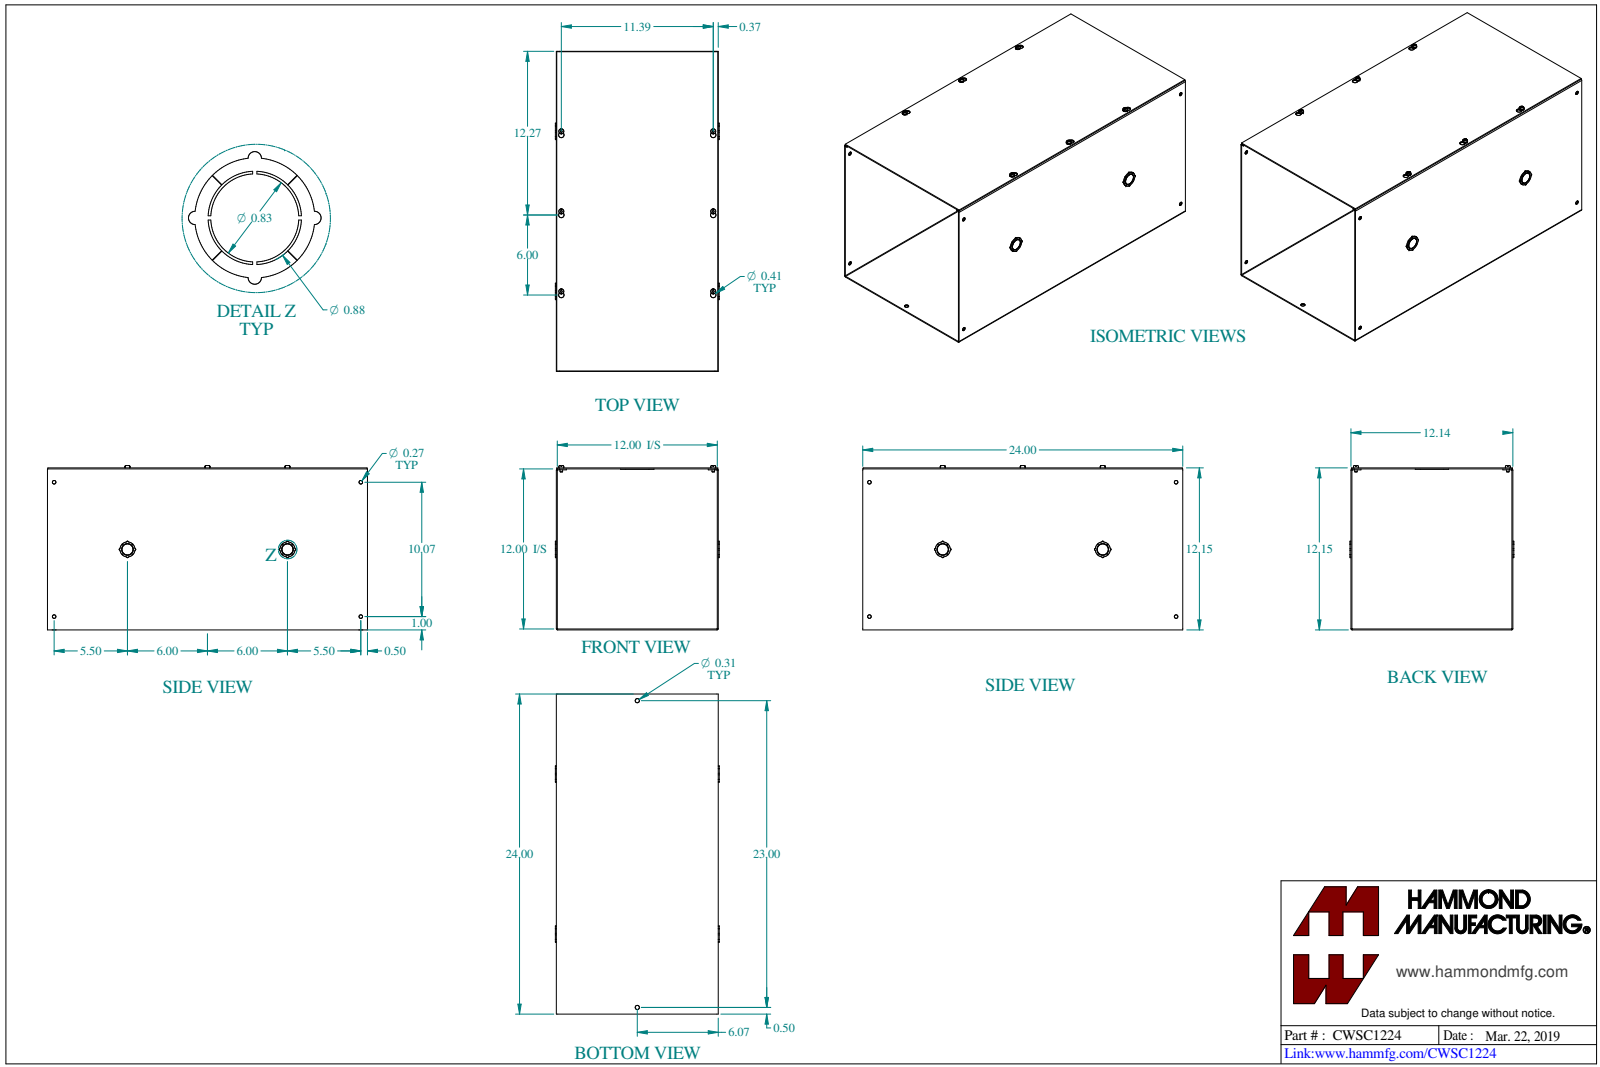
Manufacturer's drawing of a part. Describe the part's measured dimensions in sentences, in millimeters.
The part is named "CWSC1224". Its 3-D file was written by "SolidWorks 2023 (CONFIG_CONTROL_DESIGN)". It is 8 solids with 410 faces: 186 planar, 188 cylindrical and 36 other. Overall it measures 609.6 by 313.1 by 312.1 millimeters. Its volume is 1 430 000 cubic millimeters and its surface area 1 540 000 square millimeters. Round holes: 6 of diameter 4.5, 4 of diameter 6.8, 2 of diameter 8, 2 of diameter 22.2. Round bosses or shafts: 6 of diameter 9.5, 6 of diameter 4.8, 2 of diameter 28.6, 2 of diameter 21. Partial cylindrical surfaces (rounded edges, fillets, slot ends): 8 of radius 1.6, 6 of radius 3.2, 6 of radius 5.2, 4 of radius 0.9, 4 of radius 2.7. The main face-to-face distances are 1.8, 306.6, 304.8, 2, 308.5, 308.6, 306.8, 303, 3.8, 0.8. The hole center spacings are 152.4, 201.1, 326, 327.1, 462.5, 467.5, 289.4, 304.8.
